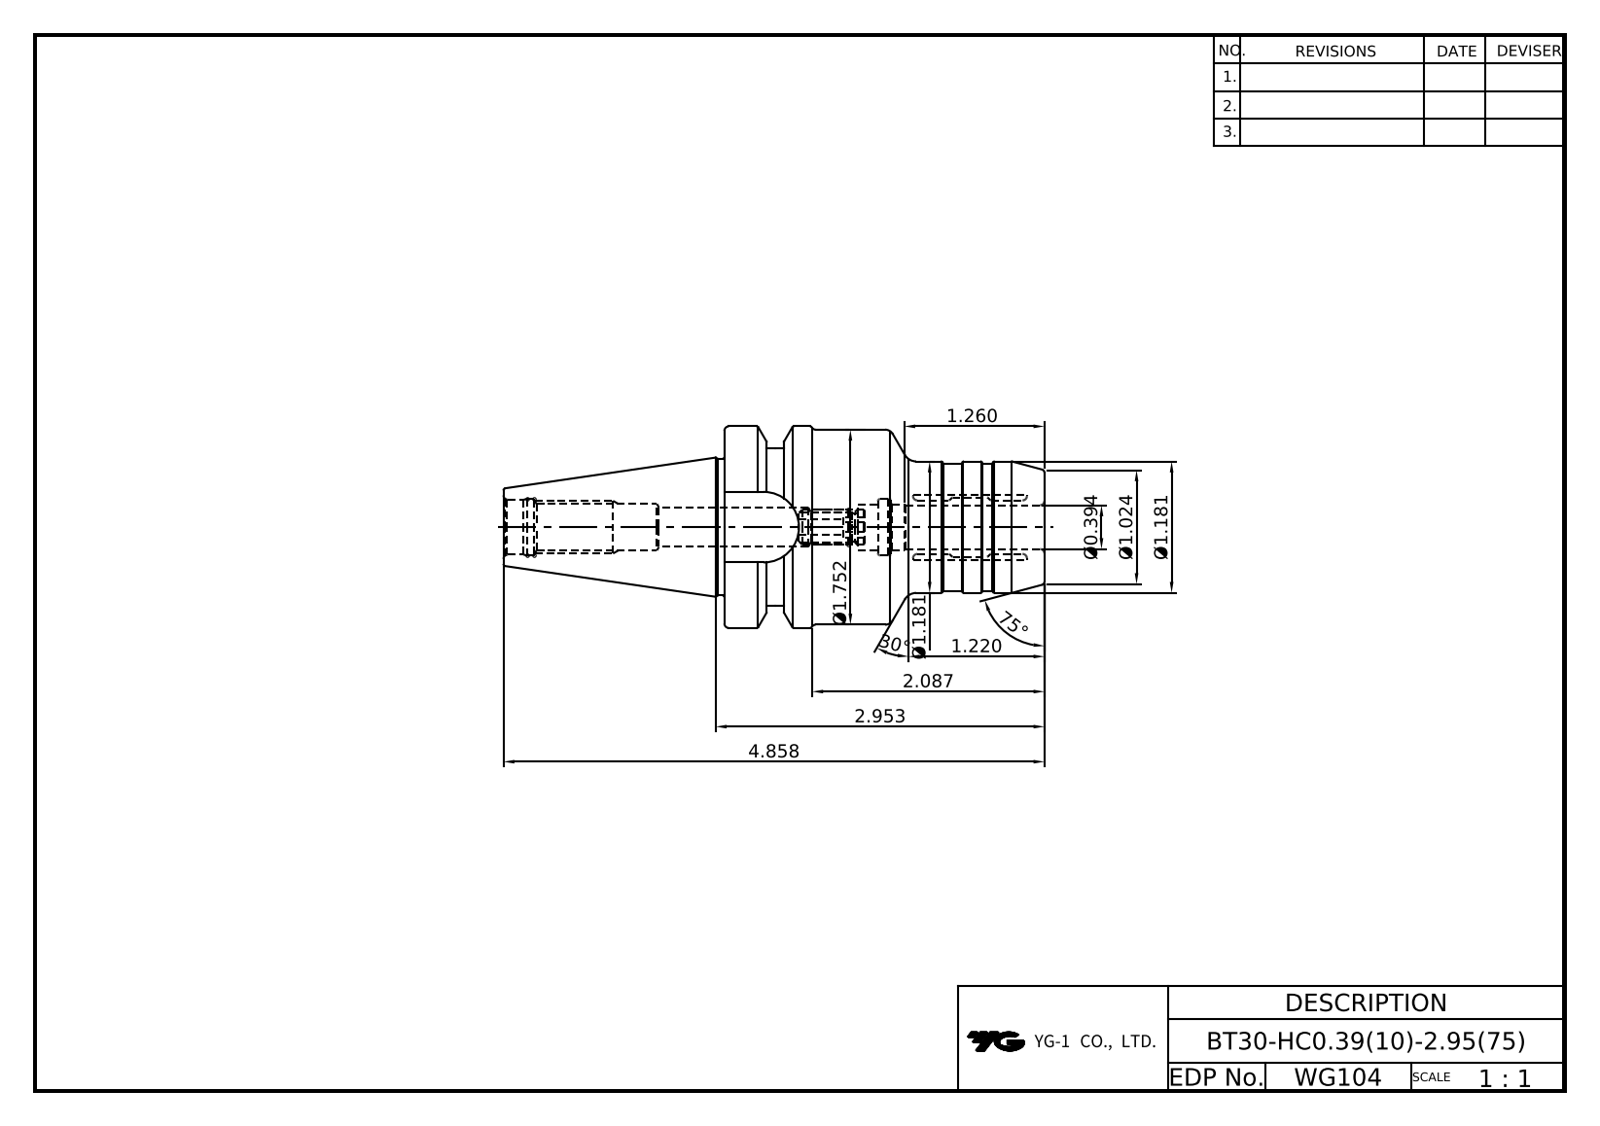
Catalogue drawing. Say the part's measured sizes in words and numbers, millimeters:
The part is named "LO-BT30ADB-HC10-75". Its 3-D file was written by "Autodesk Inventor 2022 (AUTOMOTIVE_DESIGN)". It is 1 solid with 95 faces: 20 planar, 39 cylindrical and 36 other. Overall it measures 123.4 by 46 by 46 millimeters. Its volume is 96 393 cubic millimeters and its surface area 19 738 square millimeters. Round holes: 4 of diameter 3.24, 4 of diameter 4, 1 of diameter 6.92, 1 of diameter 9, 1 of diameter 10, 1 of diameter 10.11, 1 of diameter 10.6, 1 of diameter 12.5, 1 of diameter 13.1. Round bosses or shafts: 1 of diameter 46, 1 of diameter 44.5, 1 of diameter 31.2, 1 of diameter 30, 1 of diameter 29. Partial cylindrical surfaces (rounded edges, fillets, slot ends): 1 of radius 8.05, 1 of radius 18. The main face-to-face distances are 73, 32.6, 13.6, 59.4, 9.6, 4, 63.4, 16.1, 50.4, 60.
